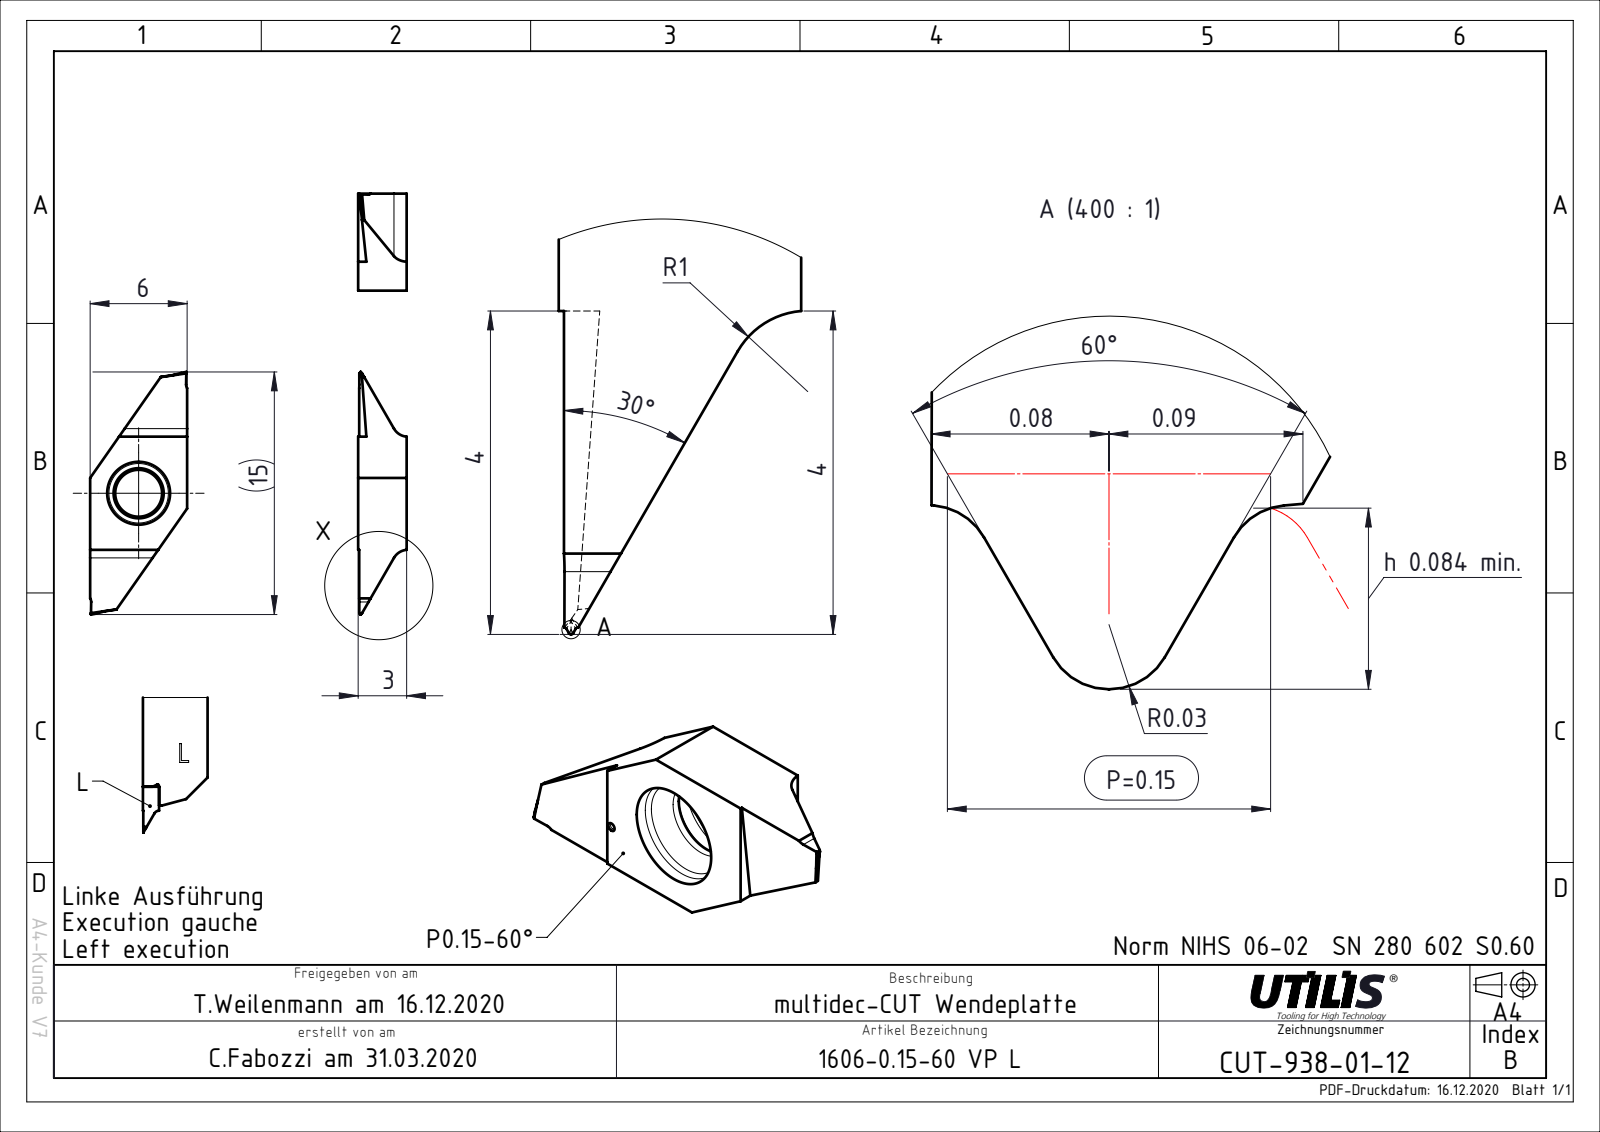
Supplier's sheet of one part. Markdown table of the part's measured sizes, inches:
| quantity | value |
| --- | --- |
| part name | CUT-938-01; ASME Y14.5 |
| STEP written by | FormatWorks Professional (AP242_MANAGED_MODEL_BASED_3D_ENGINEERING_MIM_LF) |
| units | inches |
| bodies | 1 solid, 36 faces (22 planar, 14 cylindrical, 0 other) |
| overall size | 0.591 × 0.236 × 0.118 |
| volume | 0.008 in³ |
| surface area | 0.324 in² |
| round holes (diameter × count) | 0.114 × 1 |
| partial cylindrical surfaces (radius × count) | 0.039 × 2 |
| main face-to-face distances | 0.236, 0.118, 0.354, 0.276, 0.472, 0.284, 0.283, 0.569 |
